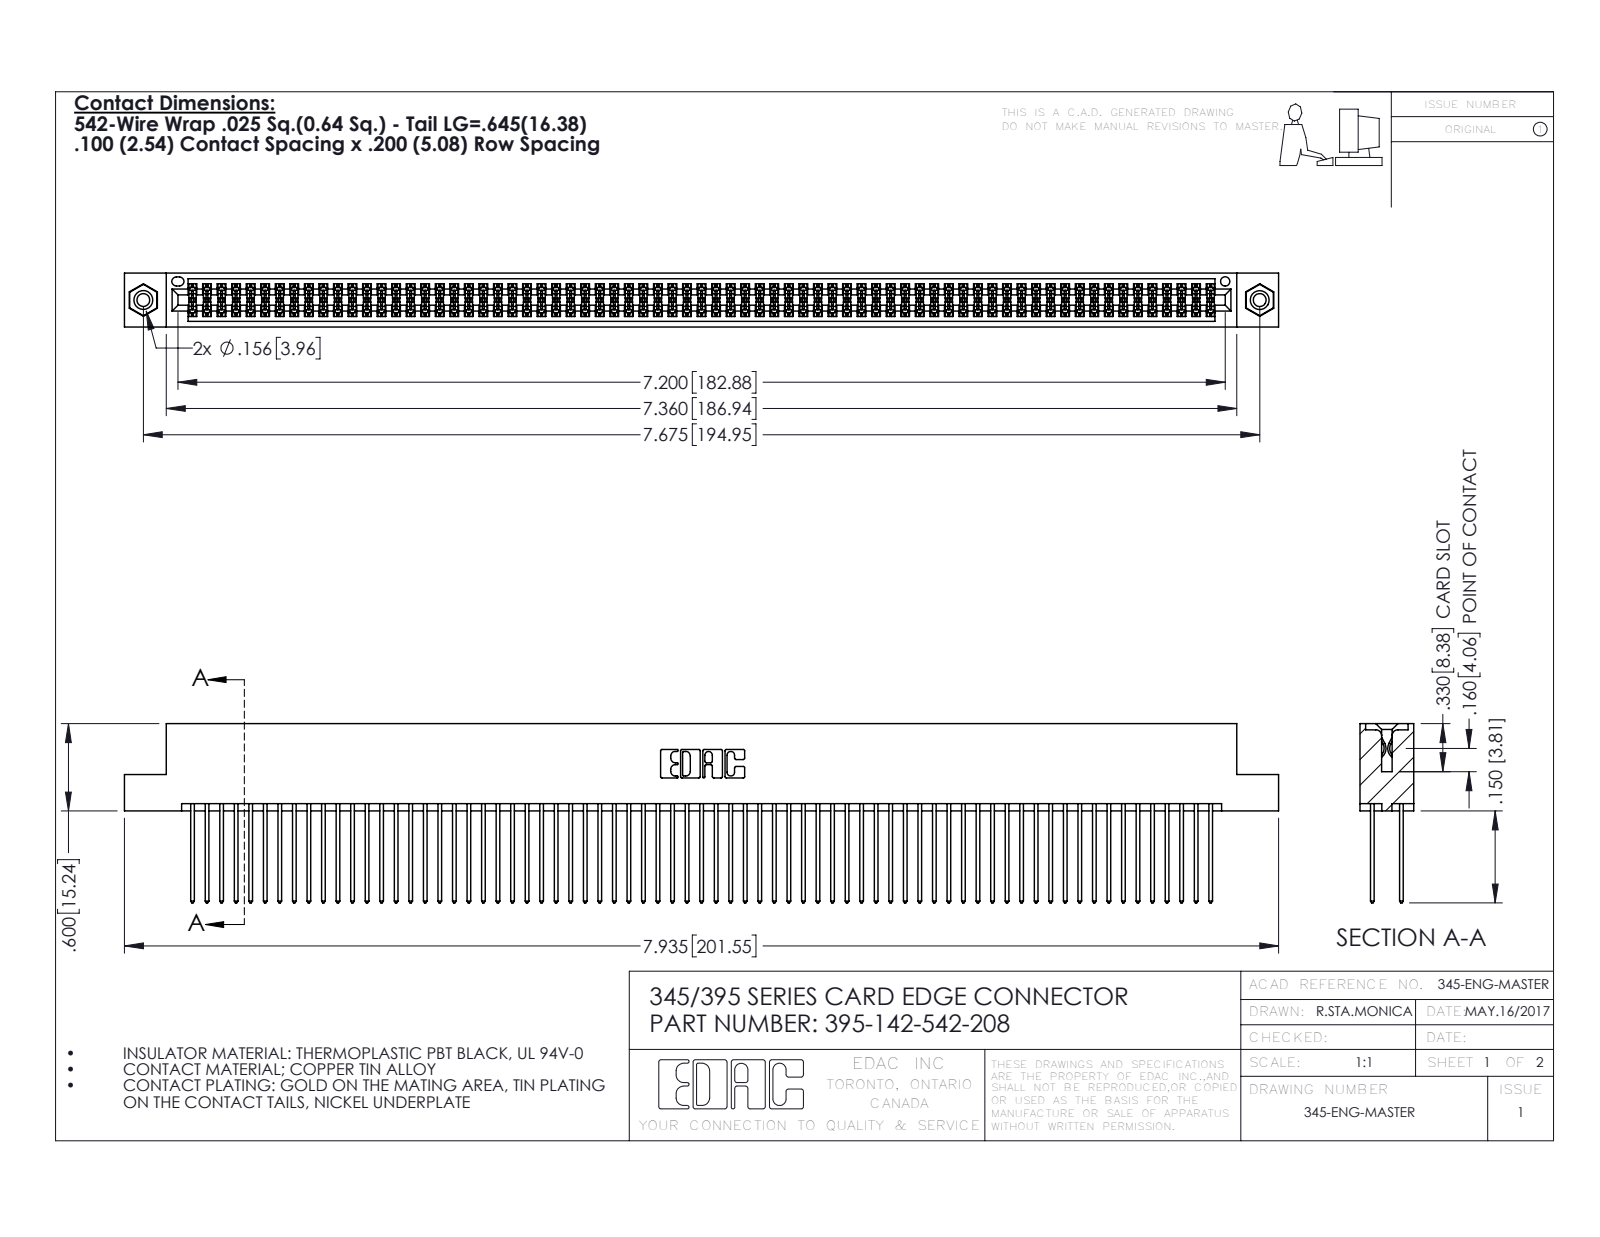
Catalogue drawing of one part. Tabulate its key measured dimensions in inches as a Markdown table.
| quantity | value |
| --- | --- |
| part name | 345 Part_Flush Mounting Lugs - 0.156 Dia-TI; 345-250-001_345-250-003-102; 345-292-001_345-293-142; 395-142-542-208 |
| STEP written by | SolidWorks 2016 (CONFIG_CONTROL_DESIGN) |
| units | inches |
| bodies | 145 solids, 7286 faces (4798 planar, 2472 cylindrical, 16 other) |
| overall size | 7.935 × 1.232 × 0.37 |
| volume | 1.251 in³ |
| surface area | 52.66 in² |
| round holes (diameter × count) | 0.089 × 2, 0.125 × 2, 0.156 × 2, 0.064 × 1 |
| round bosses / shafts (diameter × count) | 0.155 × 2 |
| partial cylindrical surfaces (radius × count) | 0.006 × 213, 0.01 × 142, 0.01 × 22, 0.007 × 6, 0.031 × 6, 0.026 × 3, 0.014 × 2, 0.019 × 2 |
| main face-to-face distances | 0.072, 0.298, 0.2, 0.098, 0.272, 0.025, 0.225, 0.37, 0.175, 0.149 |
| hole center spacings | 0.27, 7.439, 7.675 |
